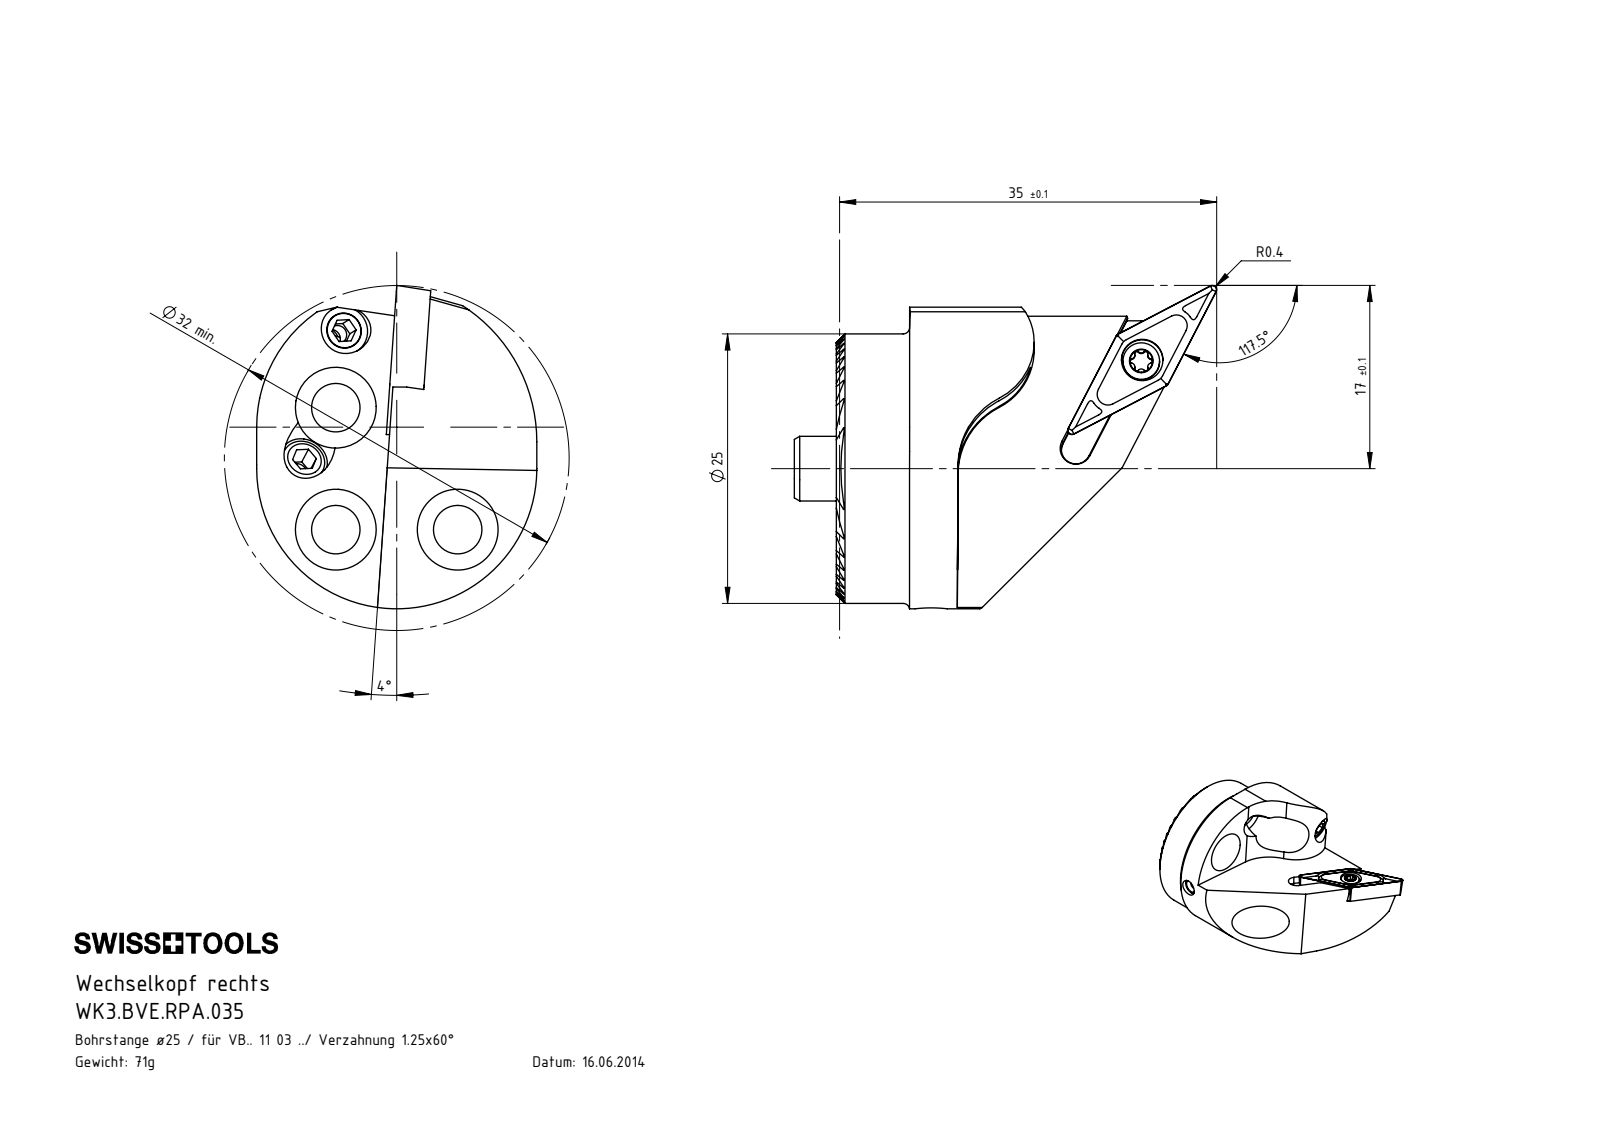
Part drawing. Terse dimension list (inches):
name: WK3-BVE.RPA.035_A_Fertigbearbeitung; VBMT110304; KVT_MB_600_030; WK3.BVE.RPA.035 (+3 more)
written by: SolidWorks 2017 (AUTOMOTIVE_DESIGN)
unit: in
bodies: 12 solids, 529 faces (181 planar, 177 cylindrical, 171 other)
size: 1.543 × 1.181 × 1.024
volume: 0.54 in³; area: 9.367 in²
holes: 5× ⌀0.177, 3× ⌀0.094, 3× ⌀0.098, 3× ⌀0.295, 2× ⌀0.067, 2× ⌀0.118, 2× ⌀0.13, 1× ⌀0.081, 1× ⌀0.11, 1× ⌀0.152, 1× ⌀0.165, 1× ⌀0.236
bosses: 3× ⌀0.118, 2× ⌀0.157, 1× ⌀0.984, 1× ⌀0.134, 1× ⌀0.098
rounds: 20× R0.005, 6× R0.008, 5× R0.014, 2× R0.276, 2× R0.512, 1× R0.014, 1× R0.053, 1× R0.236
face distances: 0.17, 0.043, 0.128, 0.213, 0.341, 0.298, 0.085, 0.085, 0.383, 0.256
hole spacings: 0.315, 0.446, 0.63
